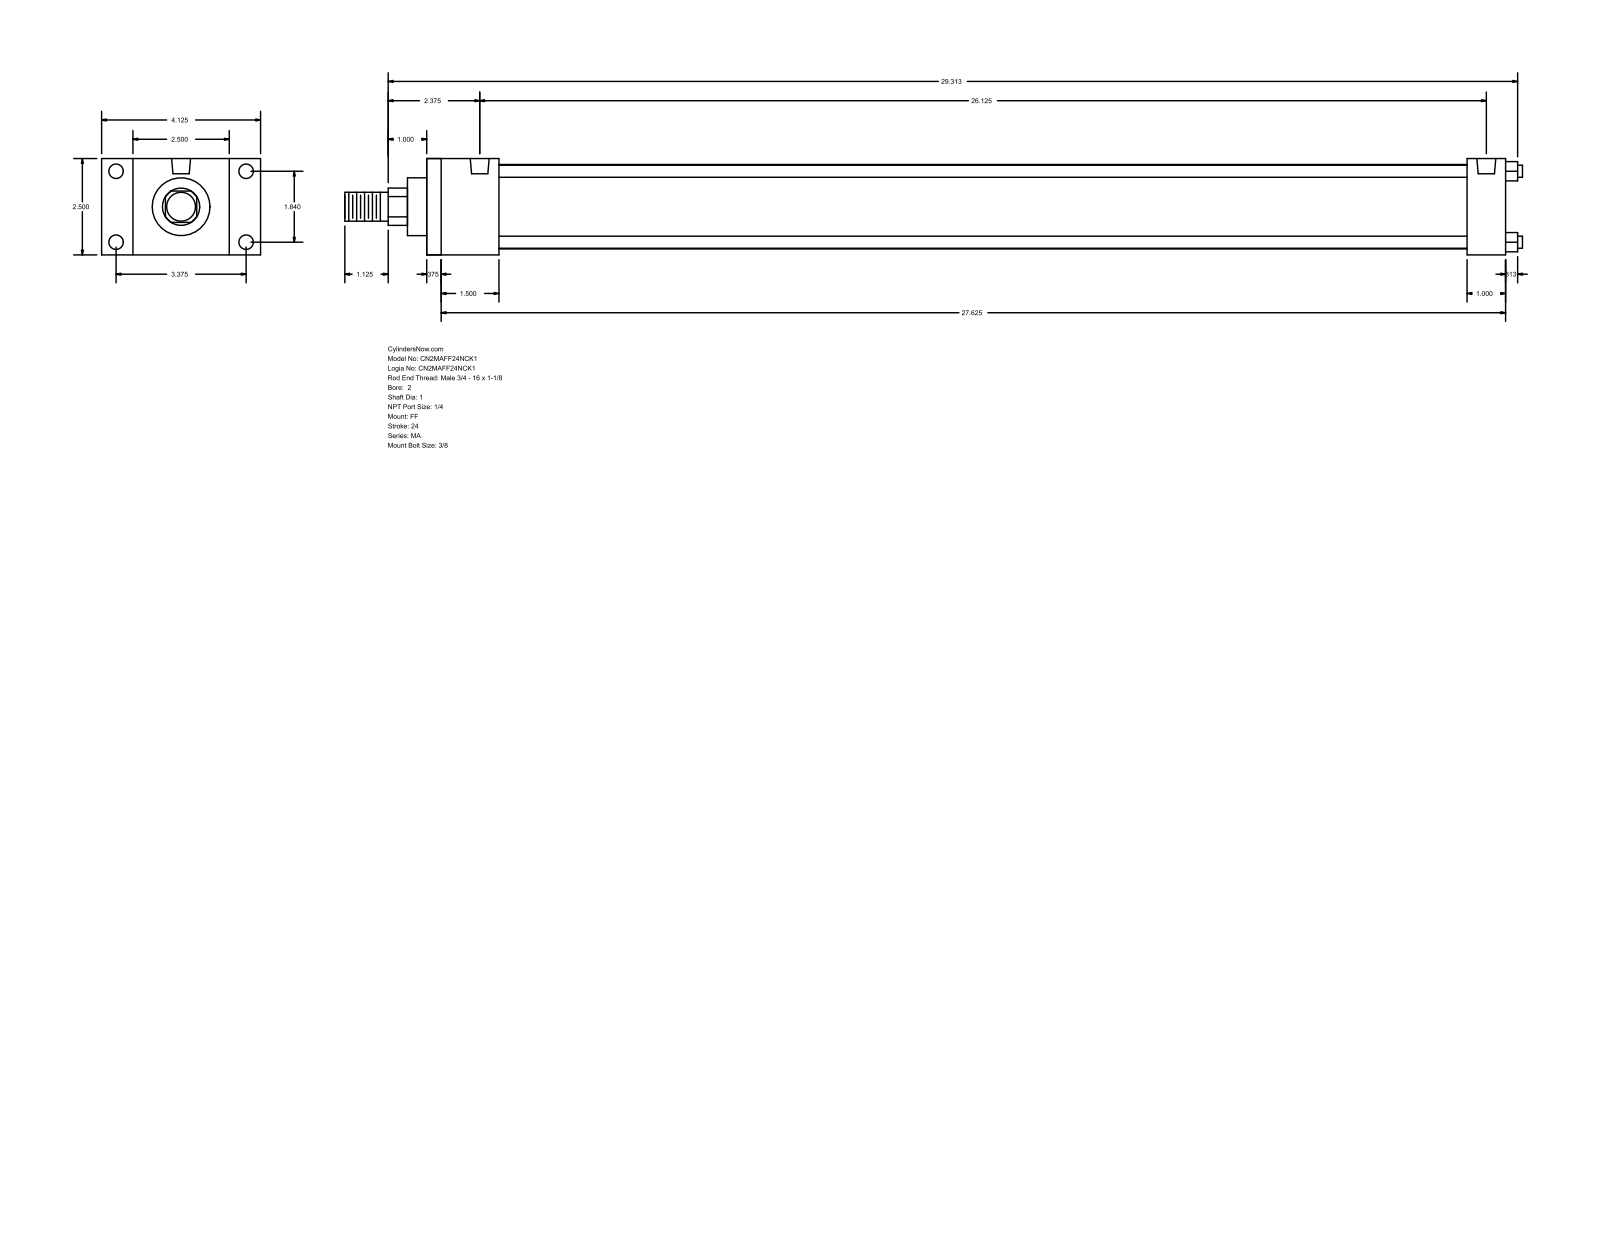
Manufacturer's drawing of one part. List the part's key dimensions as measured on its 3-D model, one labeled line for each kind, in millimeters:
Part name (STEP PRODUCT): MA_FF__0200_1
STEP written by: GSSL Pune (CONFIG_CONTROL_DESIGN)
Units: millimetres
Bodies: 0 solids, 92 faces (64 planar, 28 cylindrical, 0 other)
Overall size (bounding box): 776.29 × 104.78 × 63.5
Round holes (diameter × count): ⌀7.94 ×4, ⌀9.53 ×4, ⌀12.49 ×2
Round bosses / shafts (diameter × count): ⌀7.94 ×4, ⌀55.63 ×1, ⌀38.1 ×1, ⌀25.4 ×1, ⌀19.05 ×1
Partial cylindrical surfaces — rounded edges, fillets, slot ends (radius × count): R12.29 ×1
Main face-to-face distances: 63.5, 711.2, 9.52, 701.68, 25.4, 20.64, 12.7, 47.63, 685.8, 38.11
Hole centre spacings: 46.74, 85.72, 97.63, 663.57
